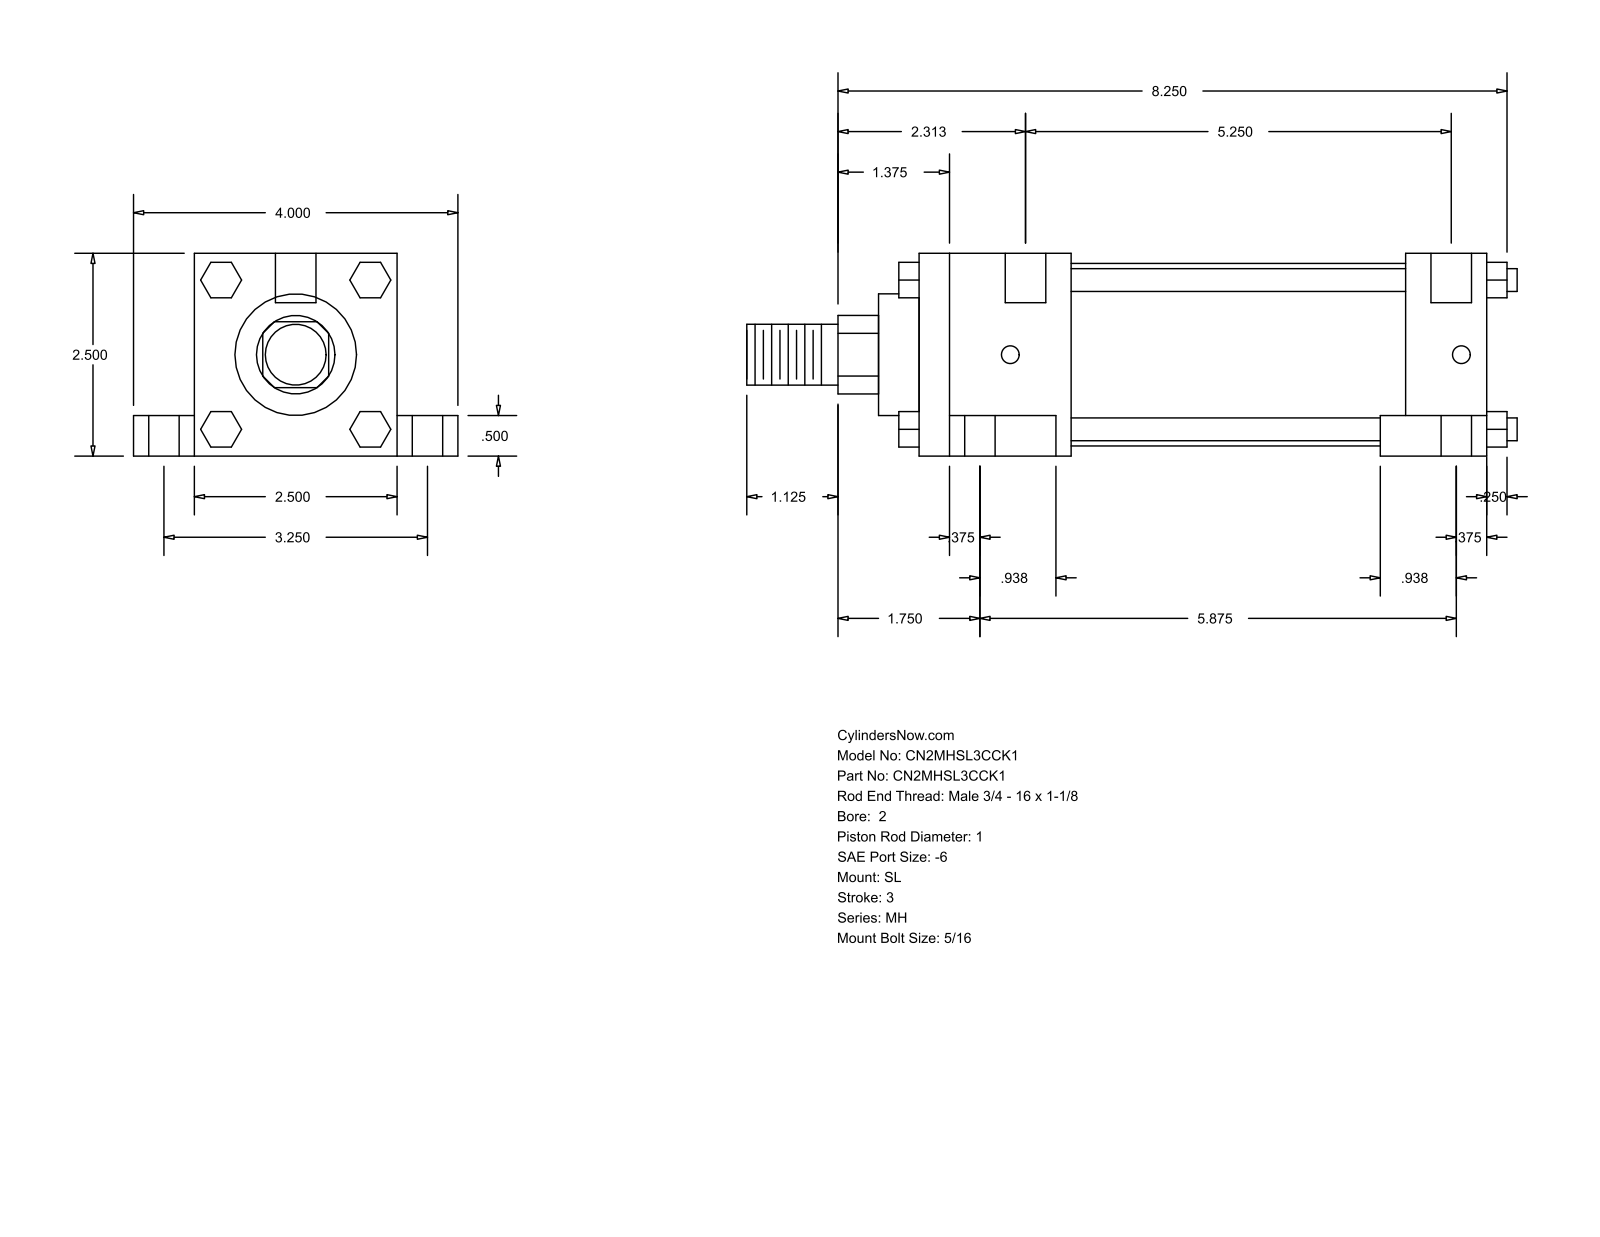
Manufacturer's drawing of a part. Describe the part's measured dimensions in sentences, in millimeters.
The part is named "MH_SL__0200_1". Its 3-D file was written by "GSSL Pune (CONFIG_CONTROL_DESIGN)". It is 0 solids with 148 faces: 112 planar, 36 cylindrical and 0 other. Overall it measures 241.3 by 101.6 by 63.5 millimeters. Round holes: 4 of diameter 5.56, 4 of diameter 9.53, 4 of diameter 15.88, 2 of diameter 12.7. Round bosses or shafts: 4 of diameter 7.14, 1 of diameter 57.15, 1 of diameter 38.1, 1 of diameter 25.4, 1 of diameter 19.05. Partial cylindrical surfaces (rounded edges, fillets, slot ends): 1 of radius 12.29. The main face-to-face distances are 63.5, 177.8, 12.7, 19.05, 50.8, 82.55, 101.6, 25.4, 152.4, 47.63. The hole center spacings are 41.3, 42.36, 43.67, 82.54, 141.11, 141.28, 145.67, 149.23.
